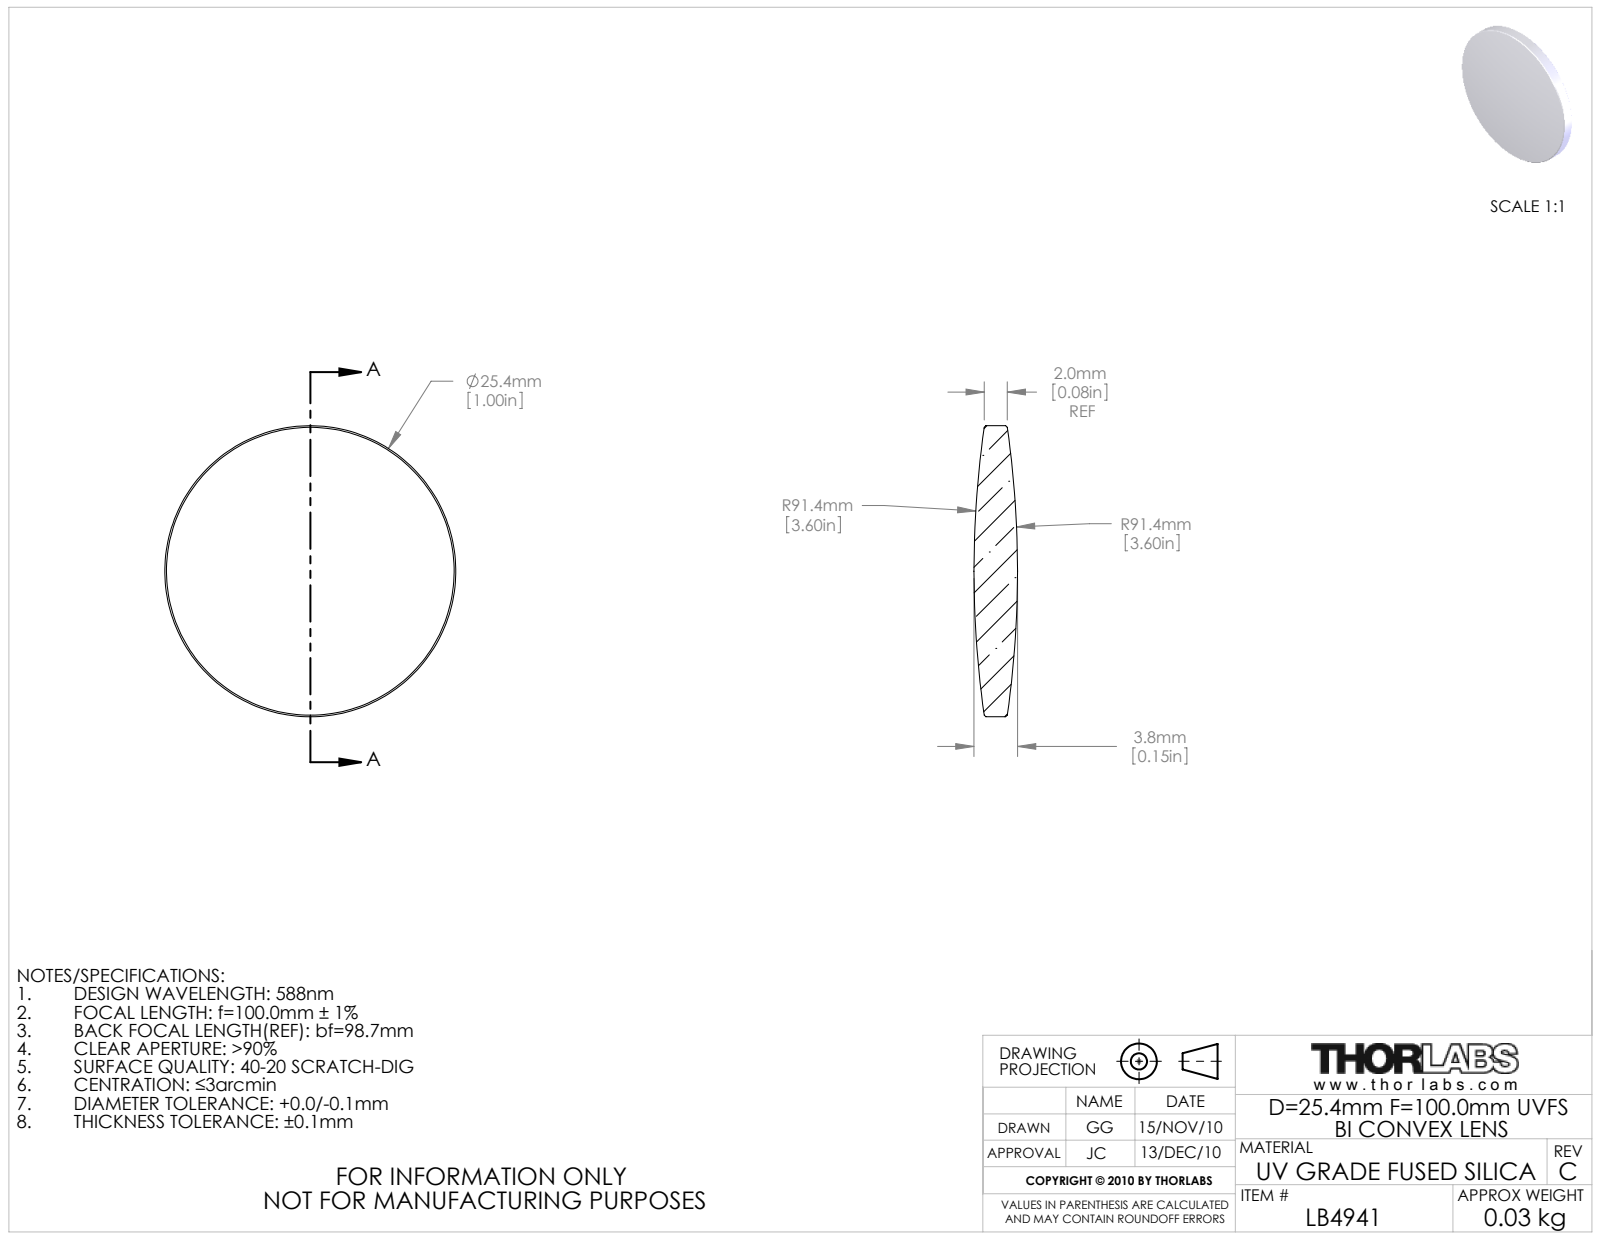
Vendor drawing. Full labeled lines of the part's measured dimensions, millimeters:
Part name (STEP PRODUCT): 3403-E0W
STEP written by: SolidWorks 2009 (AUTOMOTIVE_DESIGN)
Units: millimetres
Bodies: 1 solid, 10 faces (0 planar, 2 cylindrical, 8 other)
Overall size (bounding box): 25.4 × 25.4 × 3.8
Volume: 1 460 mm³ · Surface area: 1 166 mm²
Round bosses / shafts (diameter × count): ⌀25.4 ×1
